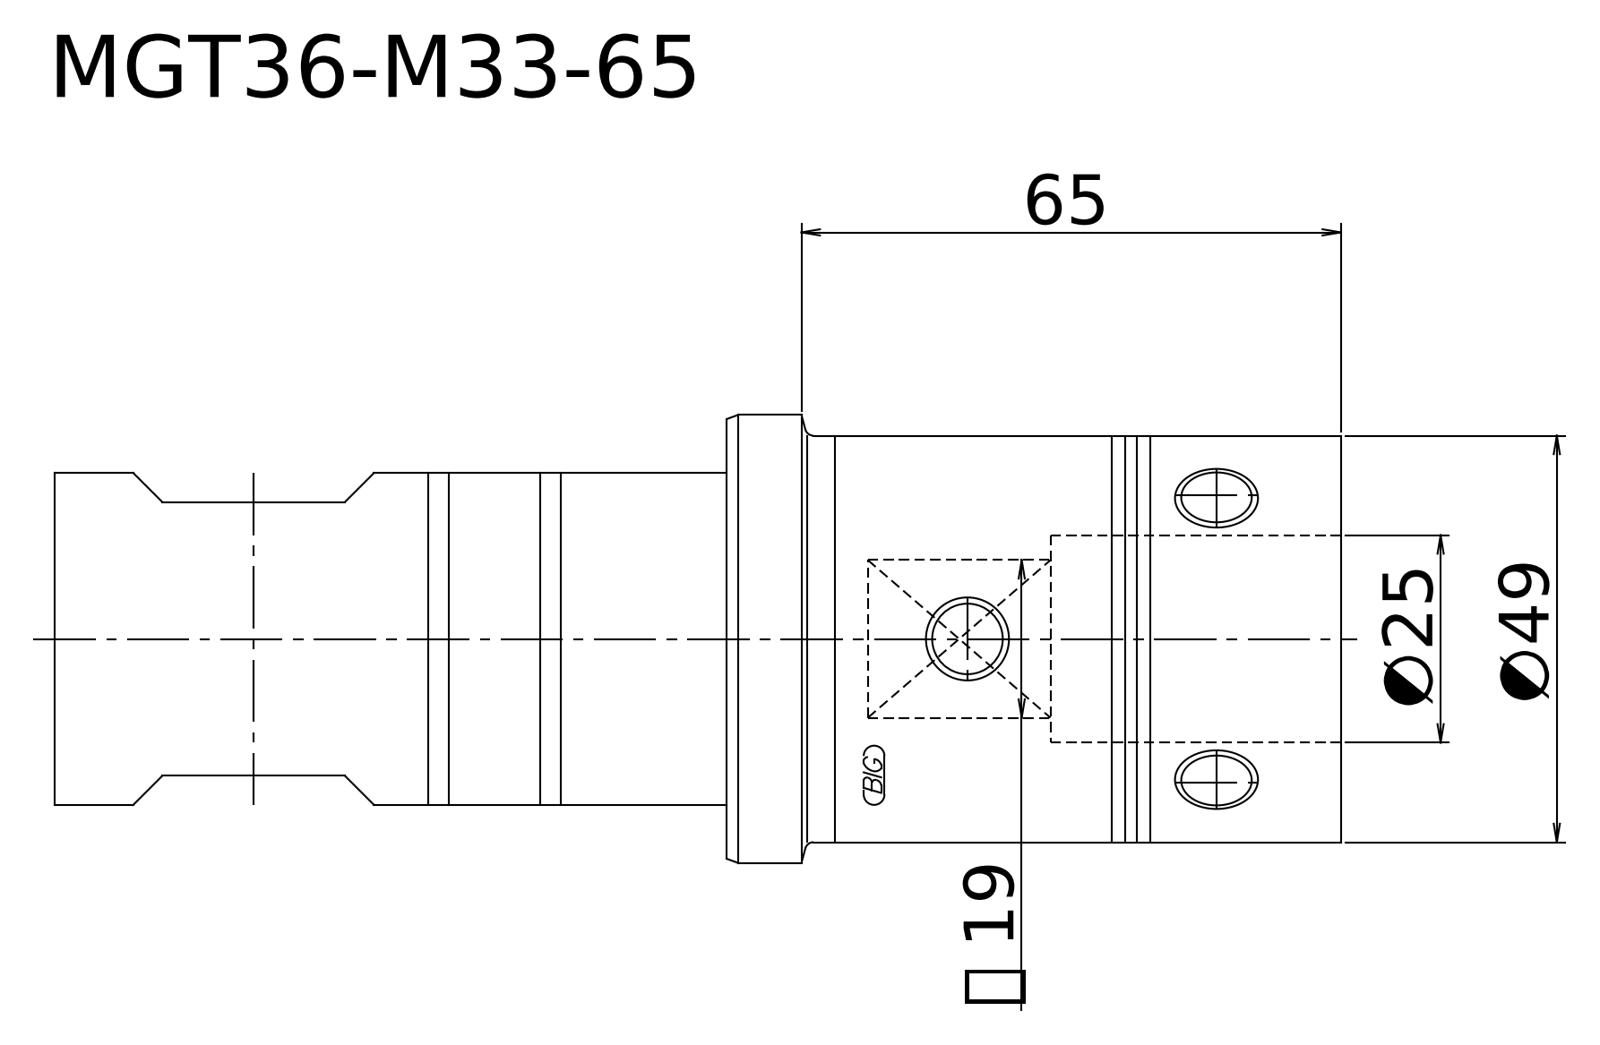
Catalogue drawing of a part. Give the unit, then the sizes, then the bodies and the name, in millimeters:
Units: millimetres
Overall size (bounding box): 240 × 54 × 54
Round bosses / shafts (diameter × count): ⌀54 ×1, ⌀49 ×1, ⌀40 ×1
Main face-to-face distances: 240, 159, 81
Volume: 405 336 mm³ · Surface area: 39 216 mm²
Bodies: 1 solid, 8 faces (3 planar, 3 cylindrical, 2 other)
Part name (STEP PRODUCT): 240[2]
STEP written by: Kubotek KeyCreator 2011 V10.0.2 (22737) (automotive_design)
